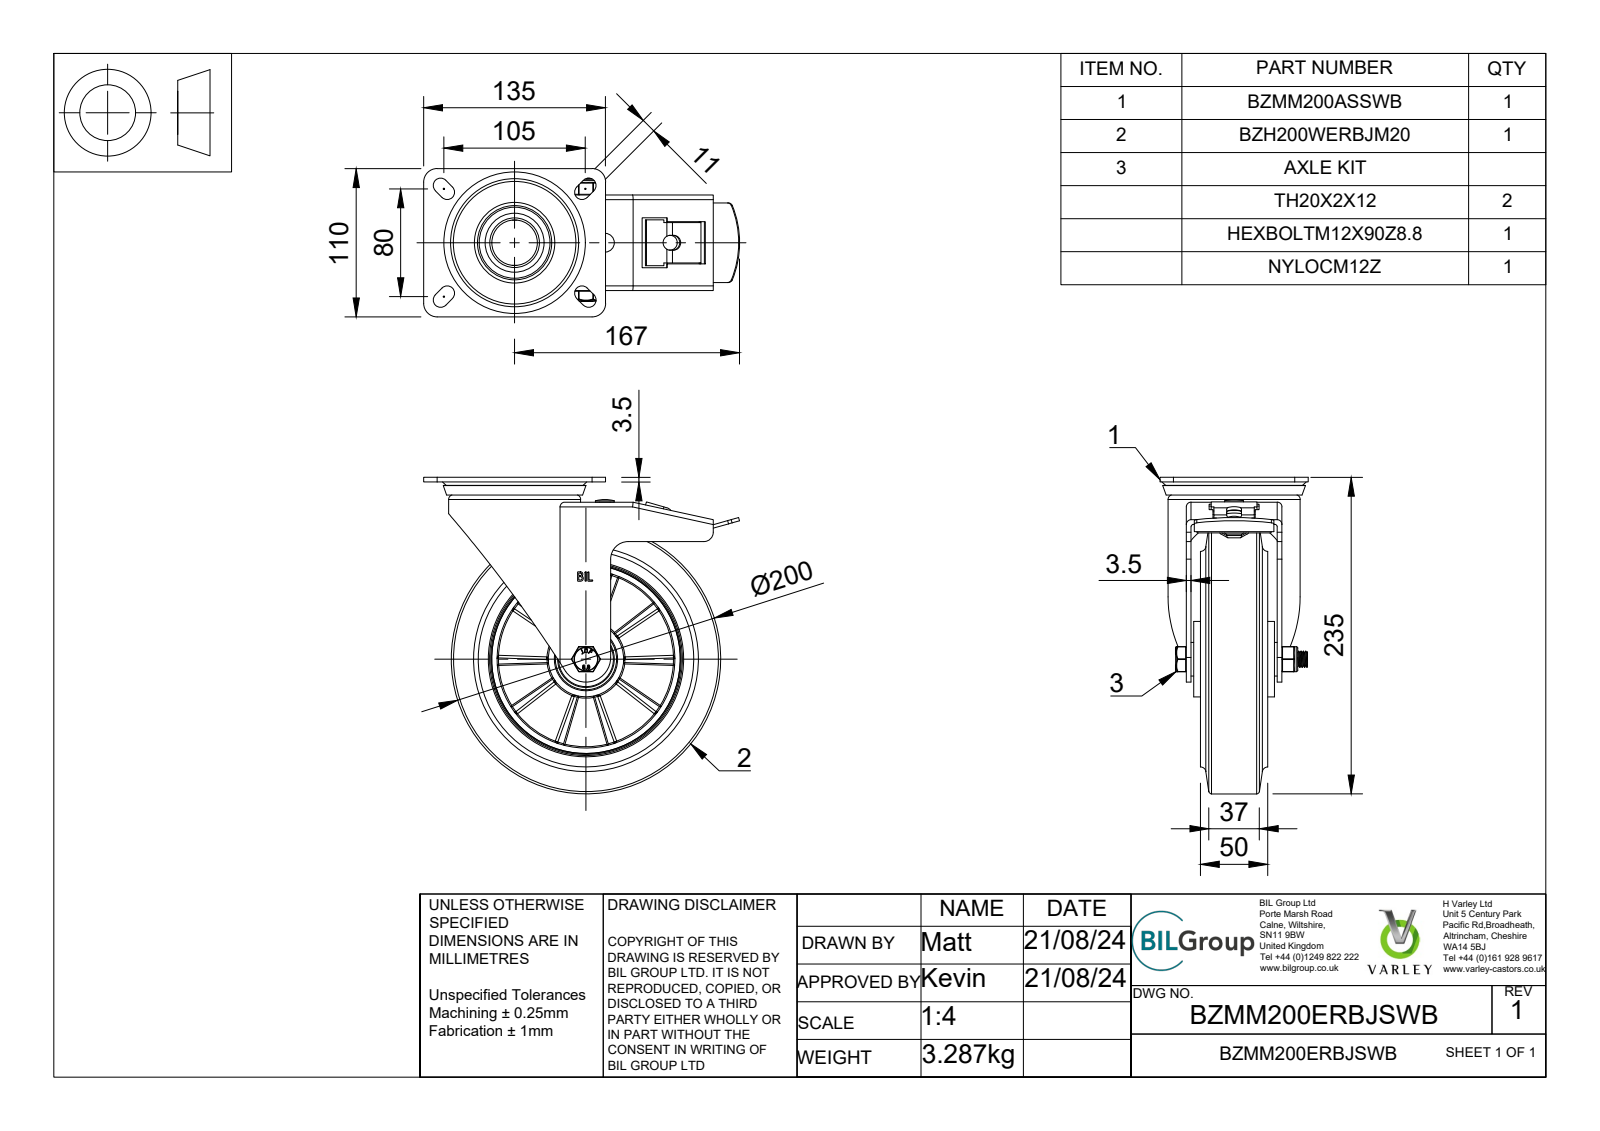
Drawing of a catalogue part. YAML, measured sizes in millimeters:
part_name: "BZMM200ERBJSWB v3; BZMM200ASSWB - 64 v1; ZINC PLATED, PRESSED STEEL TOP PLATE; ZINC PLATED, PRESSED STEEL TOP PLATE Geometry (+7 more)"
step_written_by: "Autodesk Translation Framework v13.14.0.145 (AUTOMOTIVE_DESIGN)"
units: millimeters
bodies: {solids: 82, faces: 1523, planar: 569, cylindrical: 251, other: 703}
overall_size: [235, 234.5, 110]
volume: 1168000
surface_area: 383766
round_holes:
  - {diameter: 8, count: 1}
  - {diameter: 11, count: 1}
  - {diameter: 12, count: 1}
  - {diameter: 12.2, count: 1}
  - {diameter: 14, count: 1}
  - {diameter: 20, count: 1}
  - {diameter: 28.5, count: 1}
  - {diameter: 30.8, count: 1}
  - {diameter: 33.75, count: 1}
  - {diameter: 40.3, count: 1}
  - {diameter: 40.5, count: 1}
  - {diameter: 42, count: 1}
round_bosses_or_shafts:
  - {diameter: 200, count: 1}
  - {diameter: 141.5, count: 1}
  - {diameter: 98, count: 1}
  - {diameter: 78, count: 1}
  - {diameter: 56, count: 1}
  - {diameter: 50, count: 1}
  - {diameter: 40.8, count: 1}
  - {diameter: 39.75, count: 1}
partial_cylinders:
  - {radius: 0.5, count: 19}
  - {radius: 5.5, count: 10}
  - {radius: 1.75, count: 7}
  - {radius: 0.25, count: 6}
  - {radius: 2.5, count: 6}
  - {radius: 0.47, count: 4}
  - {radius: 0.9, count: 4}
  - {radius: 3.5, count: 4}
face_to_face_distances: [3.5, 7, 50, 9, 13, 5.5, 67.5, 14, 3, 10.5]
hole_center_spacings: [67]
